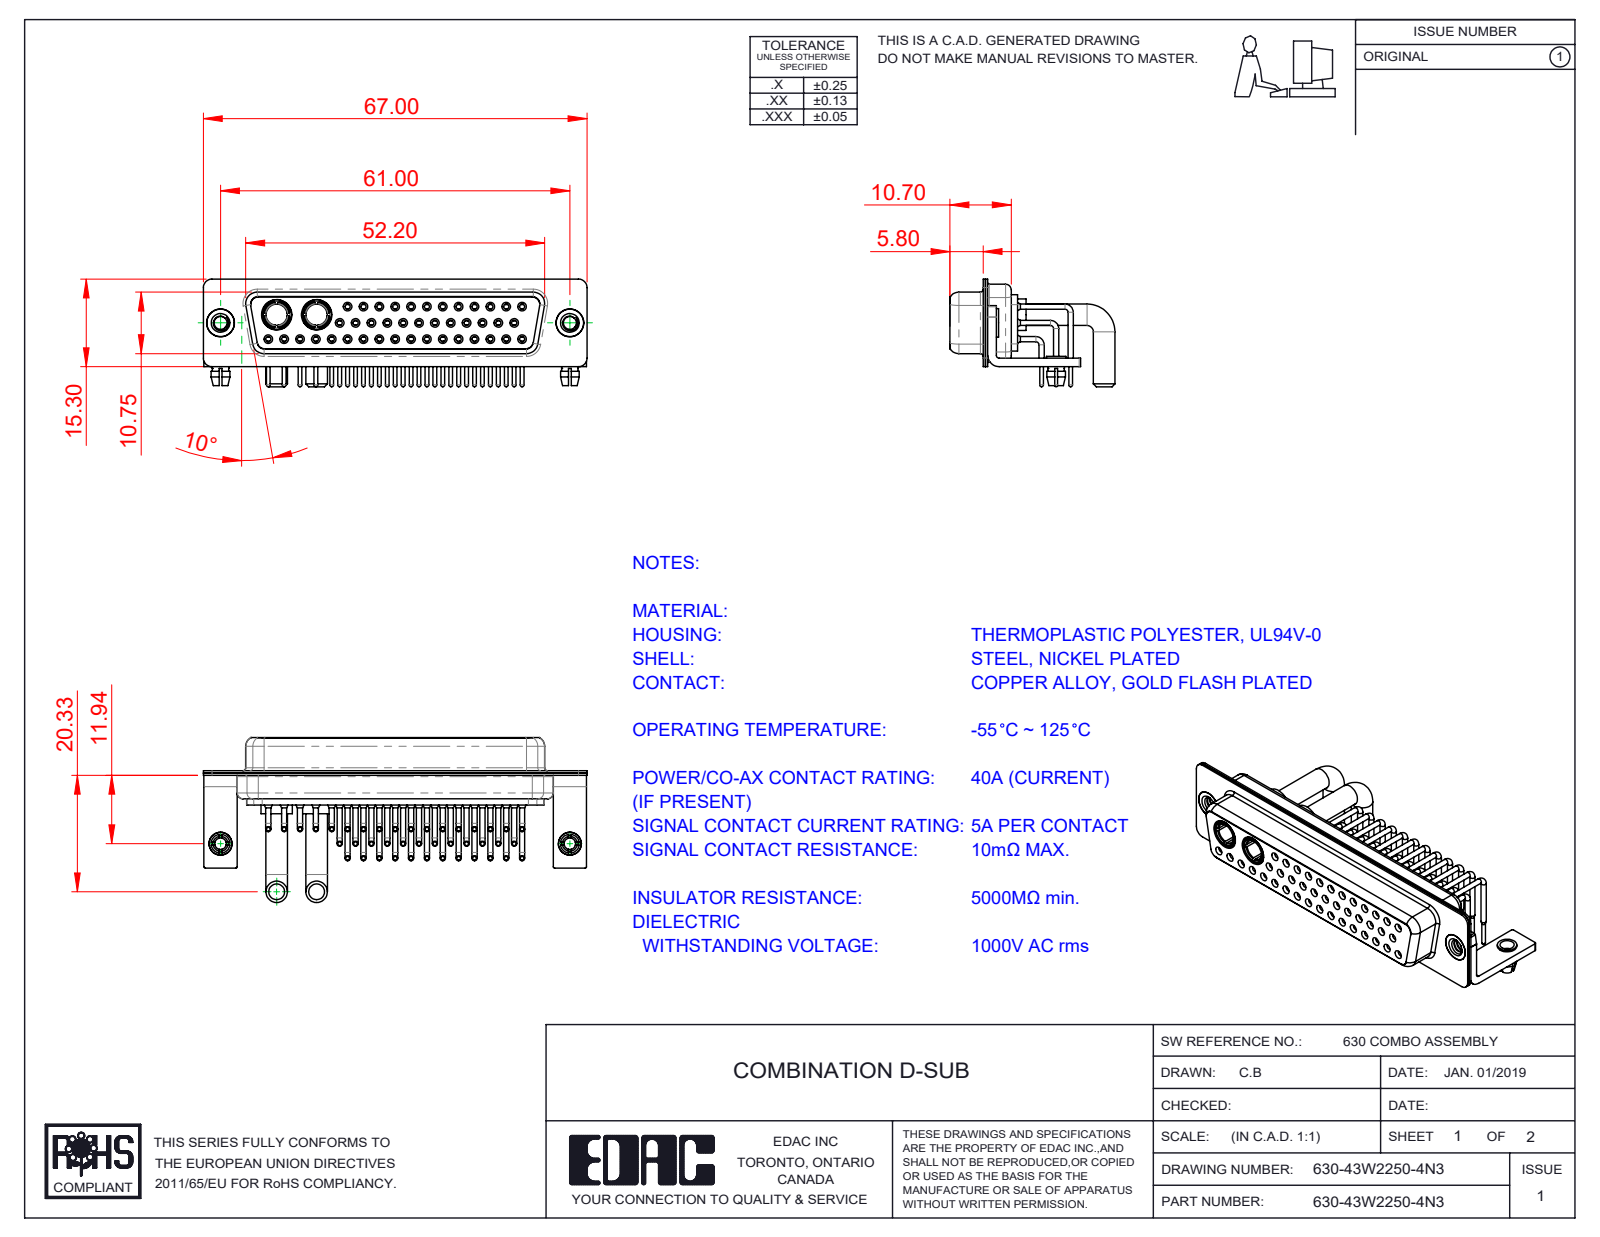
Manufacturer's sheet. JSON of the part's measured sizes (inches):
{"part_name": "630Combo Shell Front_50 Contacts; 630Combo Housing_43W2; 630Combo Contact Row 1_50 Contacts; 630Combo Contact Row 3 (+7 more)", "step_written_by": "SolidWorks 2020 (CONFIG_CONTROL_DESIGN)", "units": "inches", "bodies": {"solids": 54, "faces": 2740, "planar": 808, "cylindrical": 1180, "other": 752}, "overall_size": [2.638, 1.134, 0.74], "volume_in3": 0.484, "surface_area_in2": 26.42, "round_holes": [[0.079, 43], [0.035, 41], [0.043, 41], [0.059, 41], [0.063, 29], [0.067, 12], [0.191, 4], [0.089, 2], [0.098, 2], [0.126, 2], [0.146, 2], [0.157, 2]], "round_bosses_or_shafts": [[0.035, 41], [0.026, 41], [0.063, 12], [0.148, 4], [0.217, 2], [0.205, 2], [0.197, 2], [0.195, 2]], "partial_cylinders_radius": [[0.01, 16], [0.059, 16], [0.079, 13], [0.053, 12], [0.063, 8], [0.02, 5], [0.024, 4], [0.026, 4]], "face_to_face_distances": [0.016, 0.059, 0.236, 0.22, 0.031, 0.228, 0.205, 0.444, 0.072, 0.407], "hole_center_spacings": [0.109, 0.124, 0.218, 0.327, 0.436, 0.545, 0.654, 0.763]}
